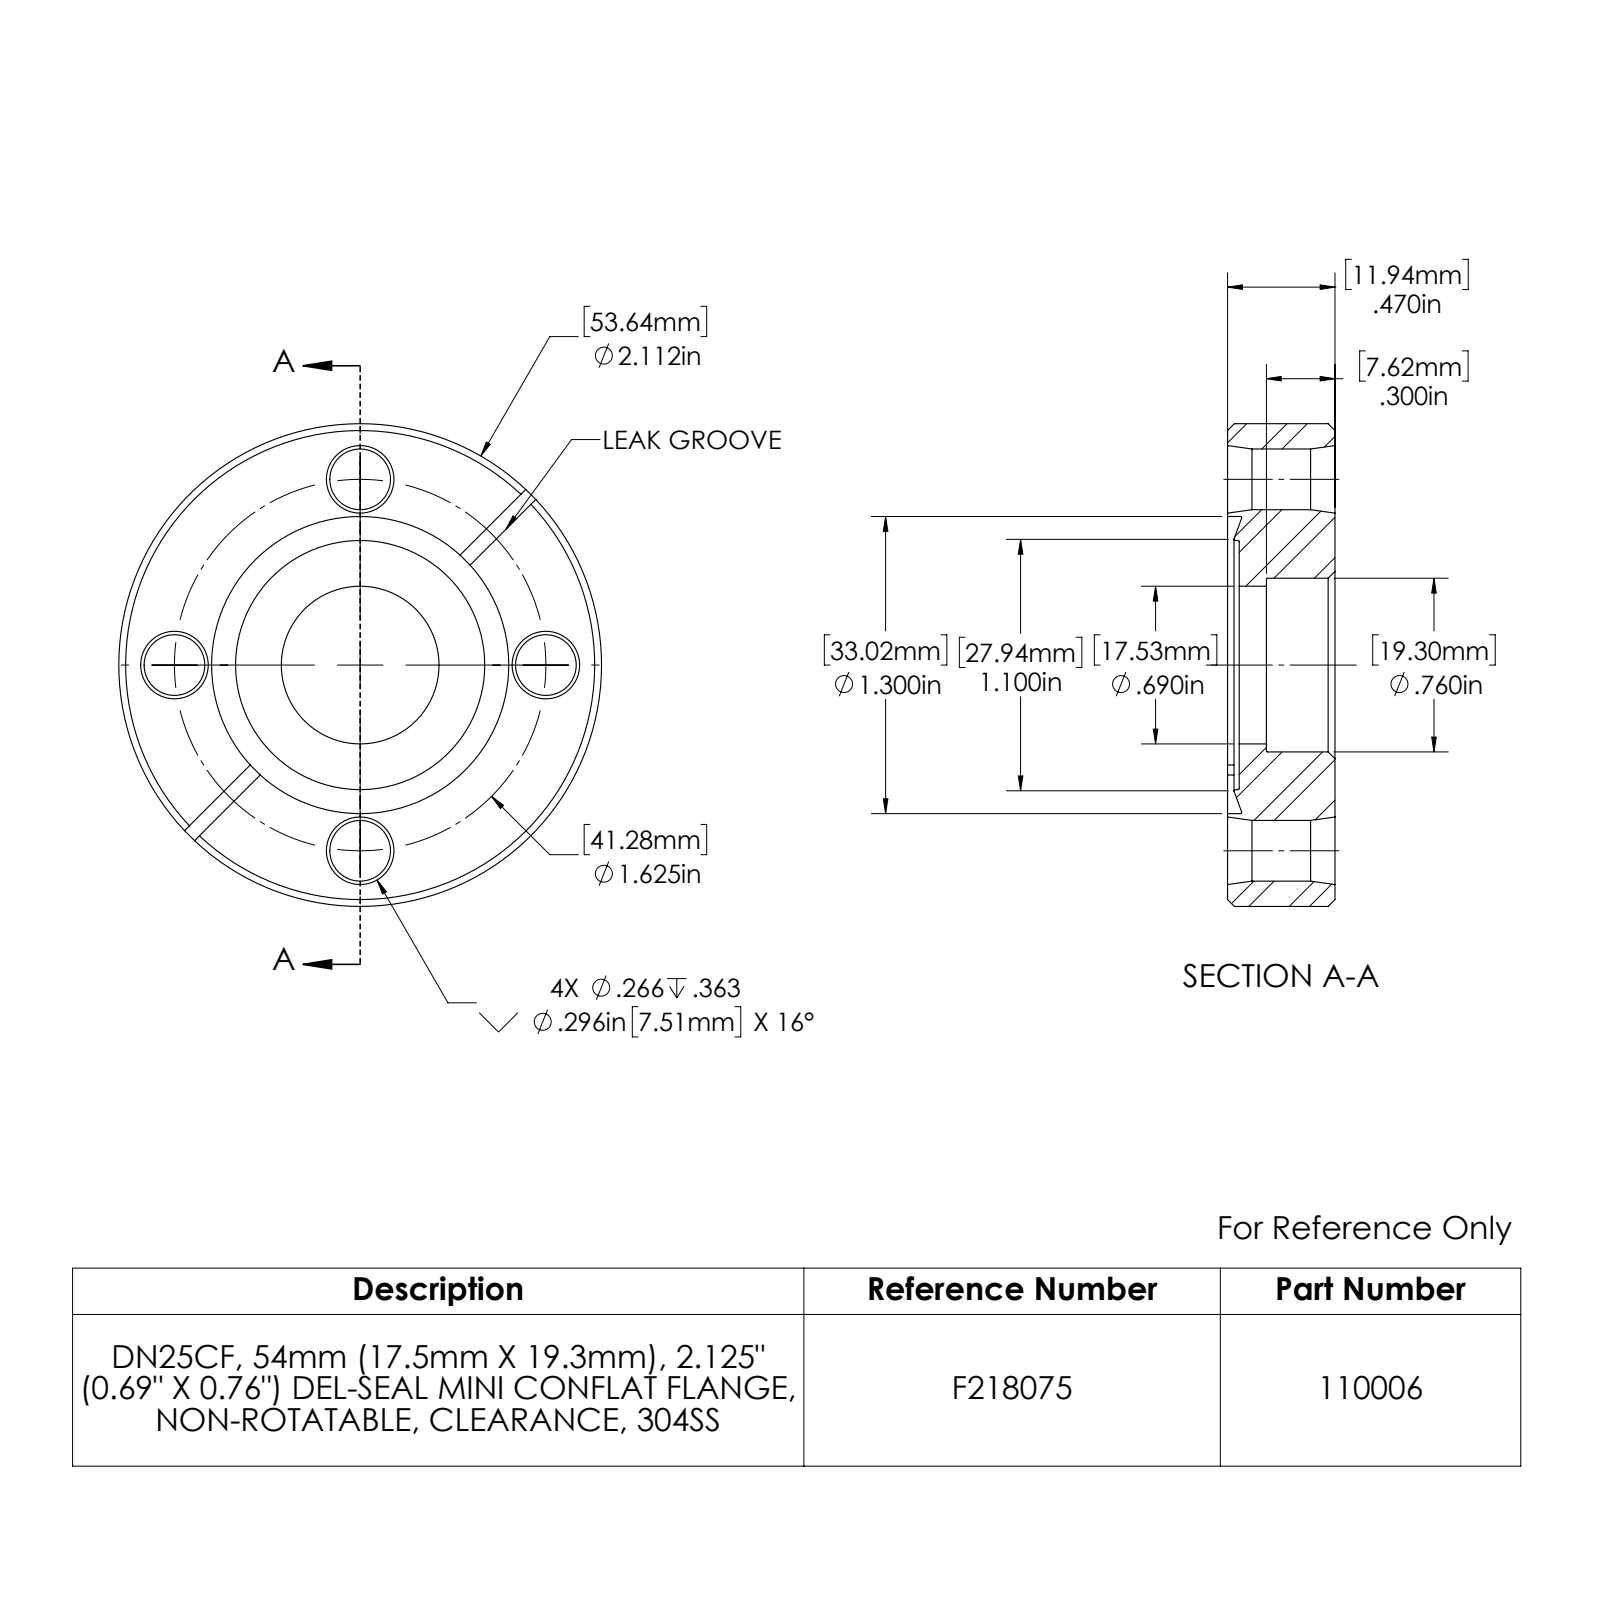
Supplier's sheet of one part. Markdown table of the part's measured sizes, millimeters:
| quantity | value |
| --- | --- |
| part name | 110006_A |
| STEP written by | SolidWorks 2022 (CONFIG_CONTROL_DESIGN) |
| units | millimeters |
| bodies | 1 solid, 62 faces (9 planar, 20 cylindrical, 33 other) |
| overall size | 53.6 × 53.6 × 11.9 |
| volume | 20 940 mm³ |
| surface area | 7 497 mm² |
| round holes (diameter × count) | 6.8 × 4, 17.5 × 1, 19.3 × 1, 27.7 × 1, 33 × 1 |
| round bosses / shafts (diameter × count) | 53.6 × 1 |
| partial cylindrical surfaces (radius × count) | 31.8 × 2 |
| main face-to-face distances | 11.9, 1.3, 10.6, 1.6, 4.3, 3, 7.6 |
| hole center spacings | 20.7, 29.2, 41.3 |
